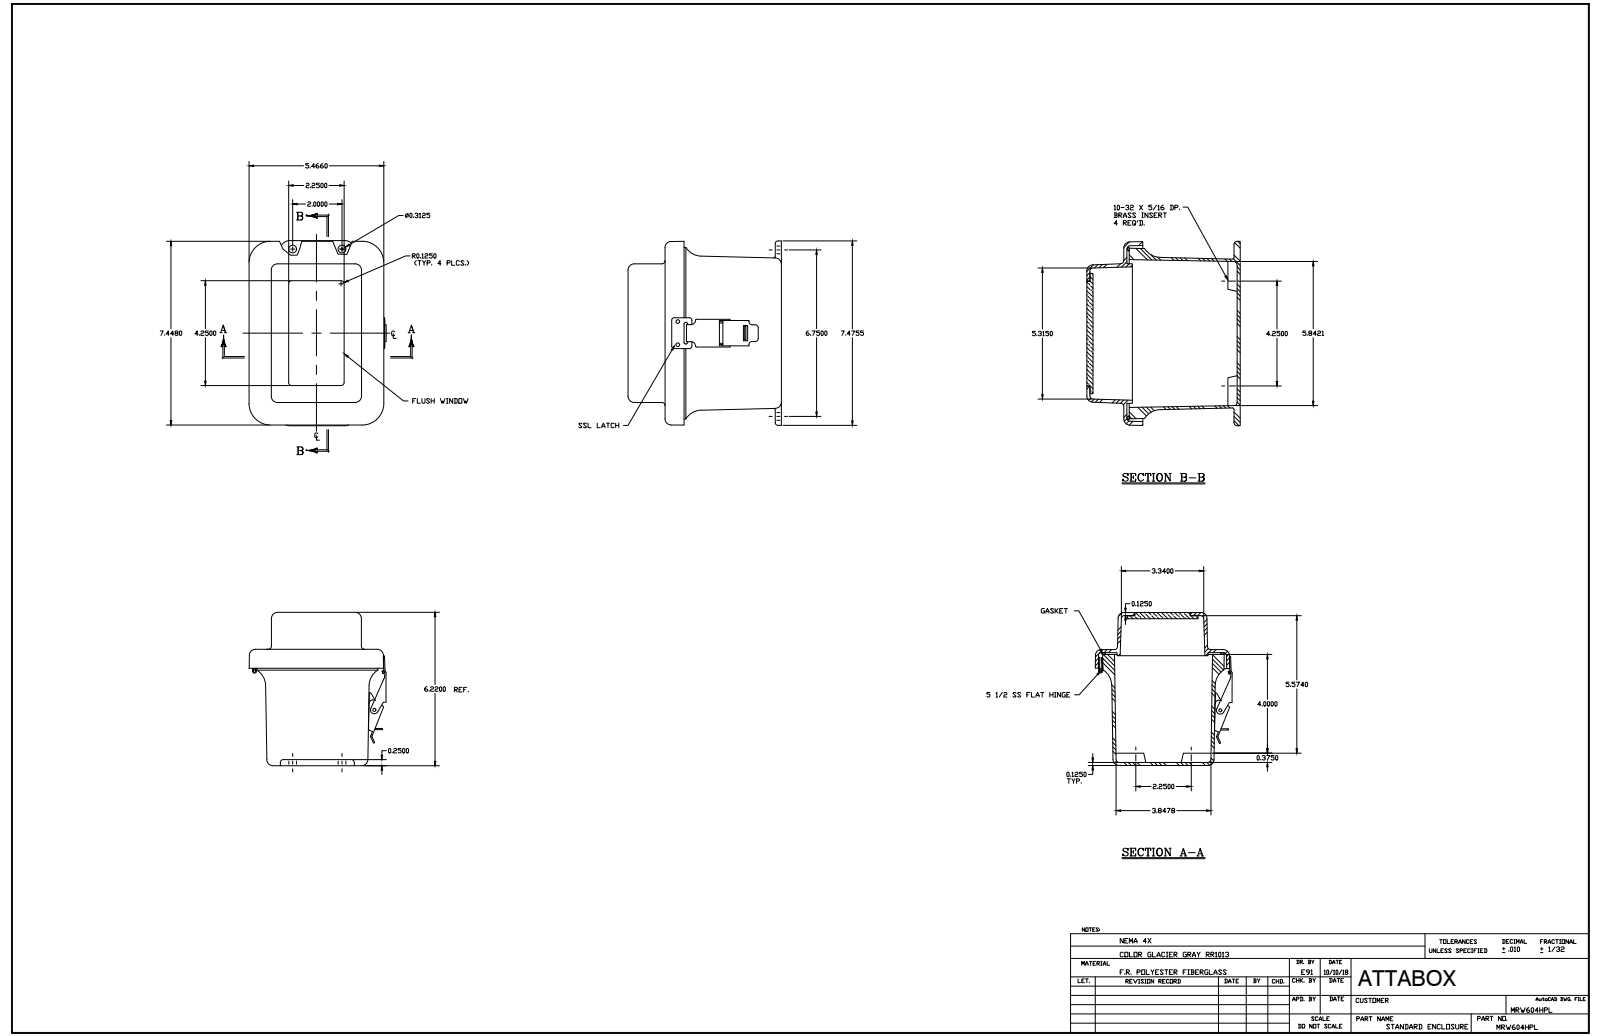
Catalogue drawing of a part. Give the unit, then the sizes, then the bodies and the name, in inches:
Units: inches
Overall size (bounding box): 7.474 × 6.227 × 5.601
Round holes (diameter × count): ⌀0.14 ×11, ⌀0.131 ×5, ⌀0.152 ×5, ⌀0.104 ×4, ⌀0.156 ×4, ⌀0.218 ×4, ⌀0.13 ×2, ⌀0.135 ×2, ⌀0.085 ×1, ⌀0.135 ×1, ⌀0.375 ×1
Round bosses / shafts (diameter × count): ⌀0.25 ×5, ⌀0.125 ×5, ⌀0.27 ×4, ⌀0.125 ×4, ⌀0.3 ×1, ⌀0.17 ×1, ⌀0.155 ×1, ⌀0.155 ×1
Partial cylindrical surfaces — rounded edges, fillets, slot ends (radius × count): R0.125 ×28, R0.031 ×20, R0.25 ×16, R0.015 ×12, R0.045 ×8, R0.03 ×6, R0.022 ×4, R0.06 ×4
Main face-to-face distances: 0.125, 4.602, 6.102, 1.5, 0.25, 0.125, 5.977, 5.852, 6.227, 1.625
Hole centre spacings: 0.937, 2.5, 3.339, 0.75, 0.469, 0.5, 1.341, 1.467
Volume: 35.44 in³ · Surface area: 474.9 in²
Bodies: 26 solids, 721 faces (287 planar, 286 cylindrical, 148 other)
Part name (STEP PRODUCT): MRW604HPL
STEP written by: SolidWorks 2018 (AUTOMOTIVE_DESIGN)
